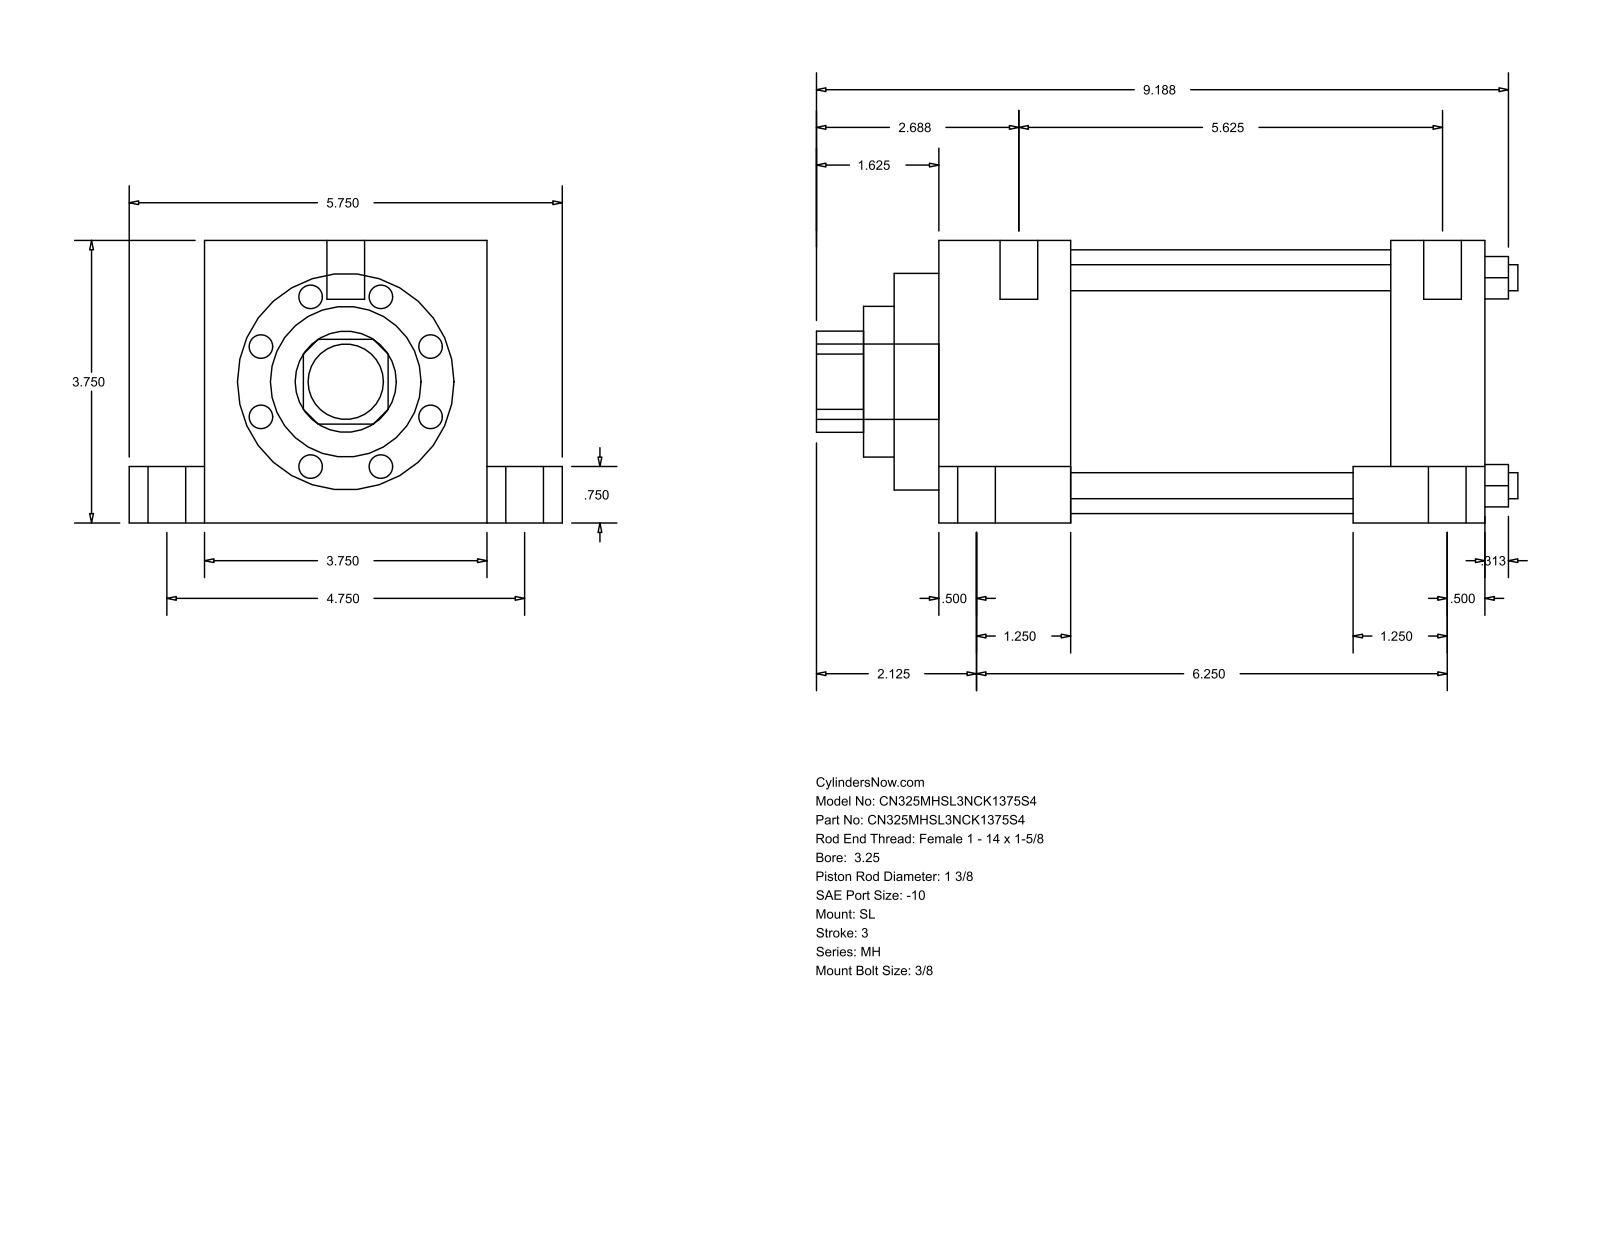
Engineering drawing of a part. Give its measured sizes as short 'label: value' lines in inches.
name: MH_SL__0325_1.375
written by: GSSL Pune (CONFIG_CONTROL_DESIGN)
unit: in
bodies: 0 solids, 110 faces (77 planar, 33 cylindrical, 0 other)
size: 9.313 × 5.75 × 3.75
holes: 4× ⌀0.345, 1× ⌀1.375, 1× ⌀2, 1× ⌀2.875, 1× ⌀3.5
bosses: 6× ⌀0.5, 4× ⌀0.75, 4× ⌀0.219, 1× ⌀1
rounds: 1× R0.672
face distances: 3.75, 7.25, 1.75, 5.5, 1, 4.75, 0.75, 3, 6, 4.25
hole spacings: 1.952, 2.76, 3.903
